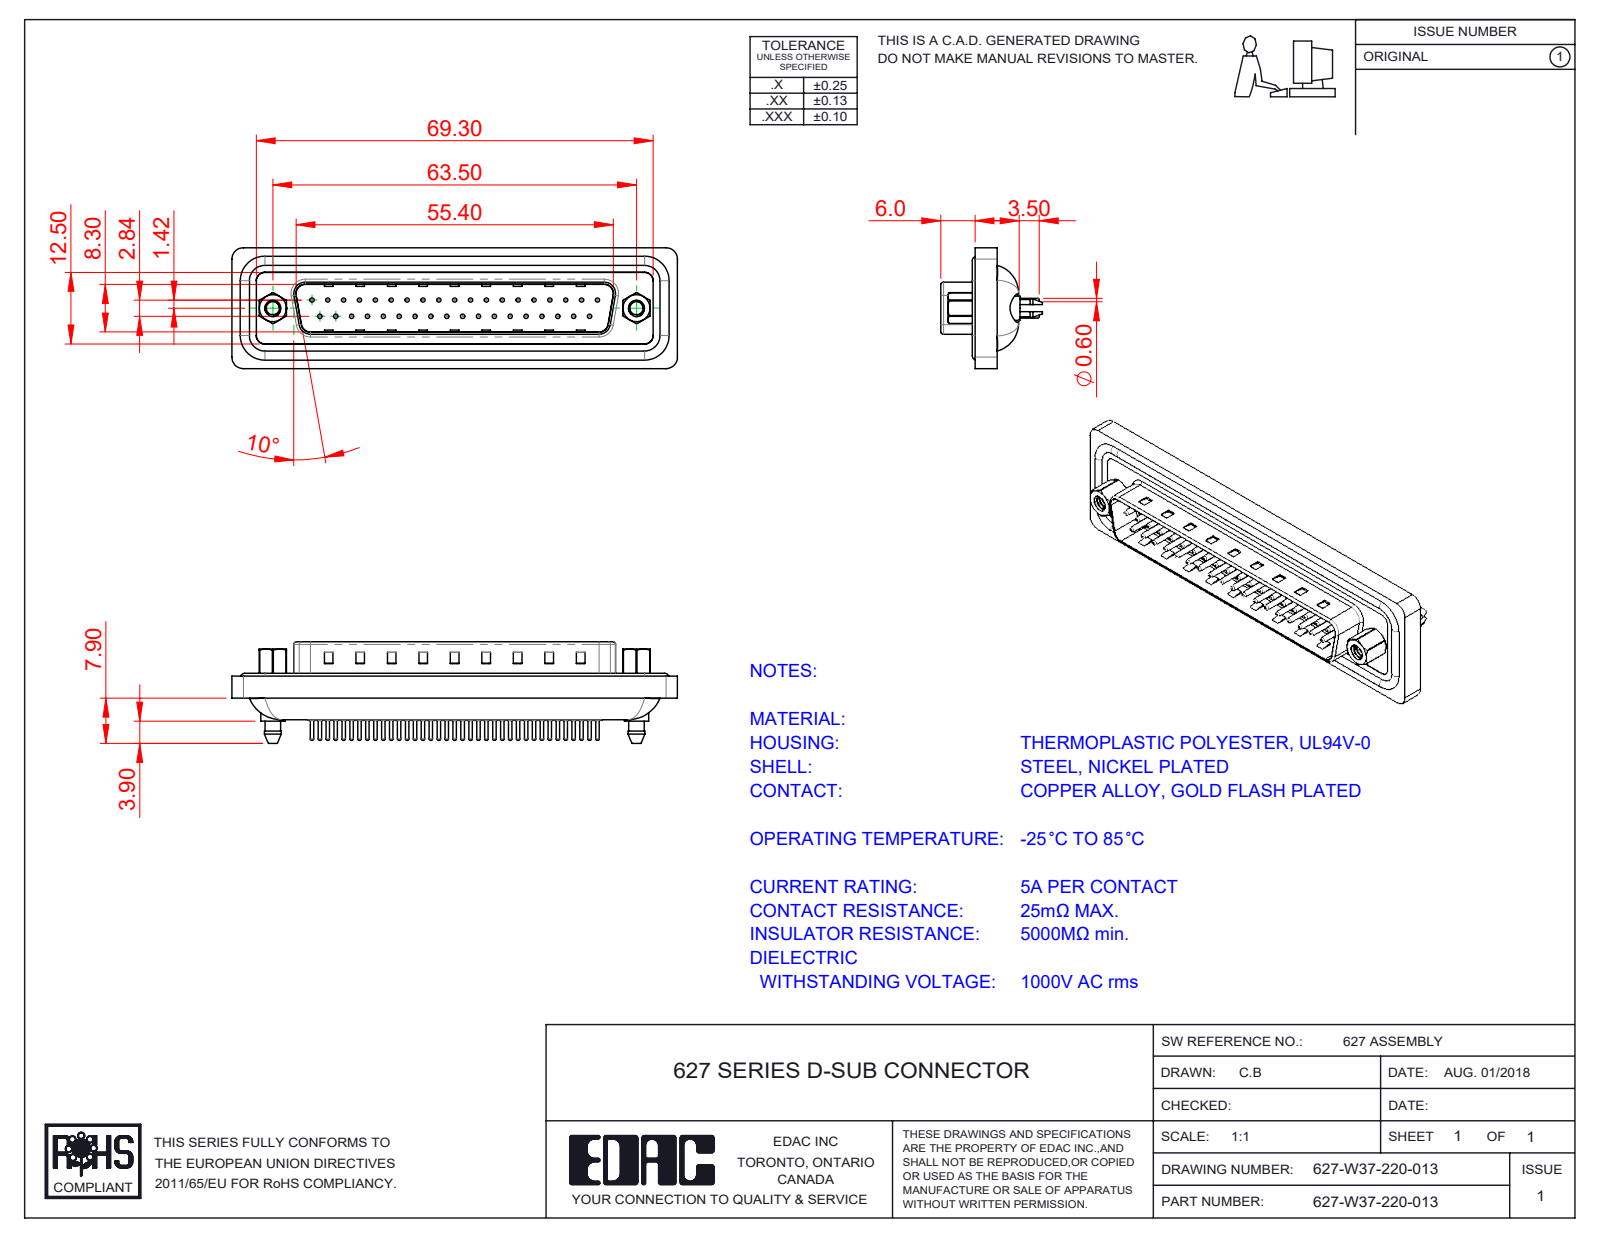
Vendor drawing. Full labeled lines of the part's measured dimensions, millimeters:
Part name (STEP PRODUCT): 627W Housing_37 Contacts; 627W Shell Front_37 Contacts; 627W Contact Row 1_20; 627W 4-40 Hex Standoff (+4 more)
STEP written by: SolidWorks 2023 (CONFIG_CONTROL_DESIGN)
Units: millimetres
Bodies: 45 solids, 2047 faces (510 planar, 848 cylindrical, 689 other)
Overall size (bounding box): 77.8 × 21.1 × 17.95
Volume: 9 541 mm³ · Surface area: 14 743 mm²
Round holes (diameter × count): ⌀0.75 ×37, ⌀1.5 ×37, ⌀1.6 ×37, ⌀2 ×37, ⌀2.26 ×2, ⌀2.29 ×2, ⌀4 ×2, ⌀4.8 ×2, ⌀5 ×2
Round bosses / shafts (diameter × count): ⌀0.6 ×37, ⌀1.5 ×9, ⌀1.6 ×4, ⌀5.4 ×2, ⌀4.9 ×2, ⌀4.25 ×2, ⌀2.79 ×2
Partial cylindrical surfaces — rounded edges, fillets, slot ends (radius × count): R1.5 ×16, R2 ×16, R0.5 ×8, R1.6 ×6, R0.9 ×4, R2.7 ×4, R4.3 ×4, R0.4 ×2
Main face-to-face distances: 0.75, 0.4, 4.1, 1.1, 2.75, 5.65, 4.6, 15.45, 3.75, 14.7
Hole centre spacings: 3.16, 2.77, 5.54, 8.31, 5.04, 10.1, 11.08, 12.78
